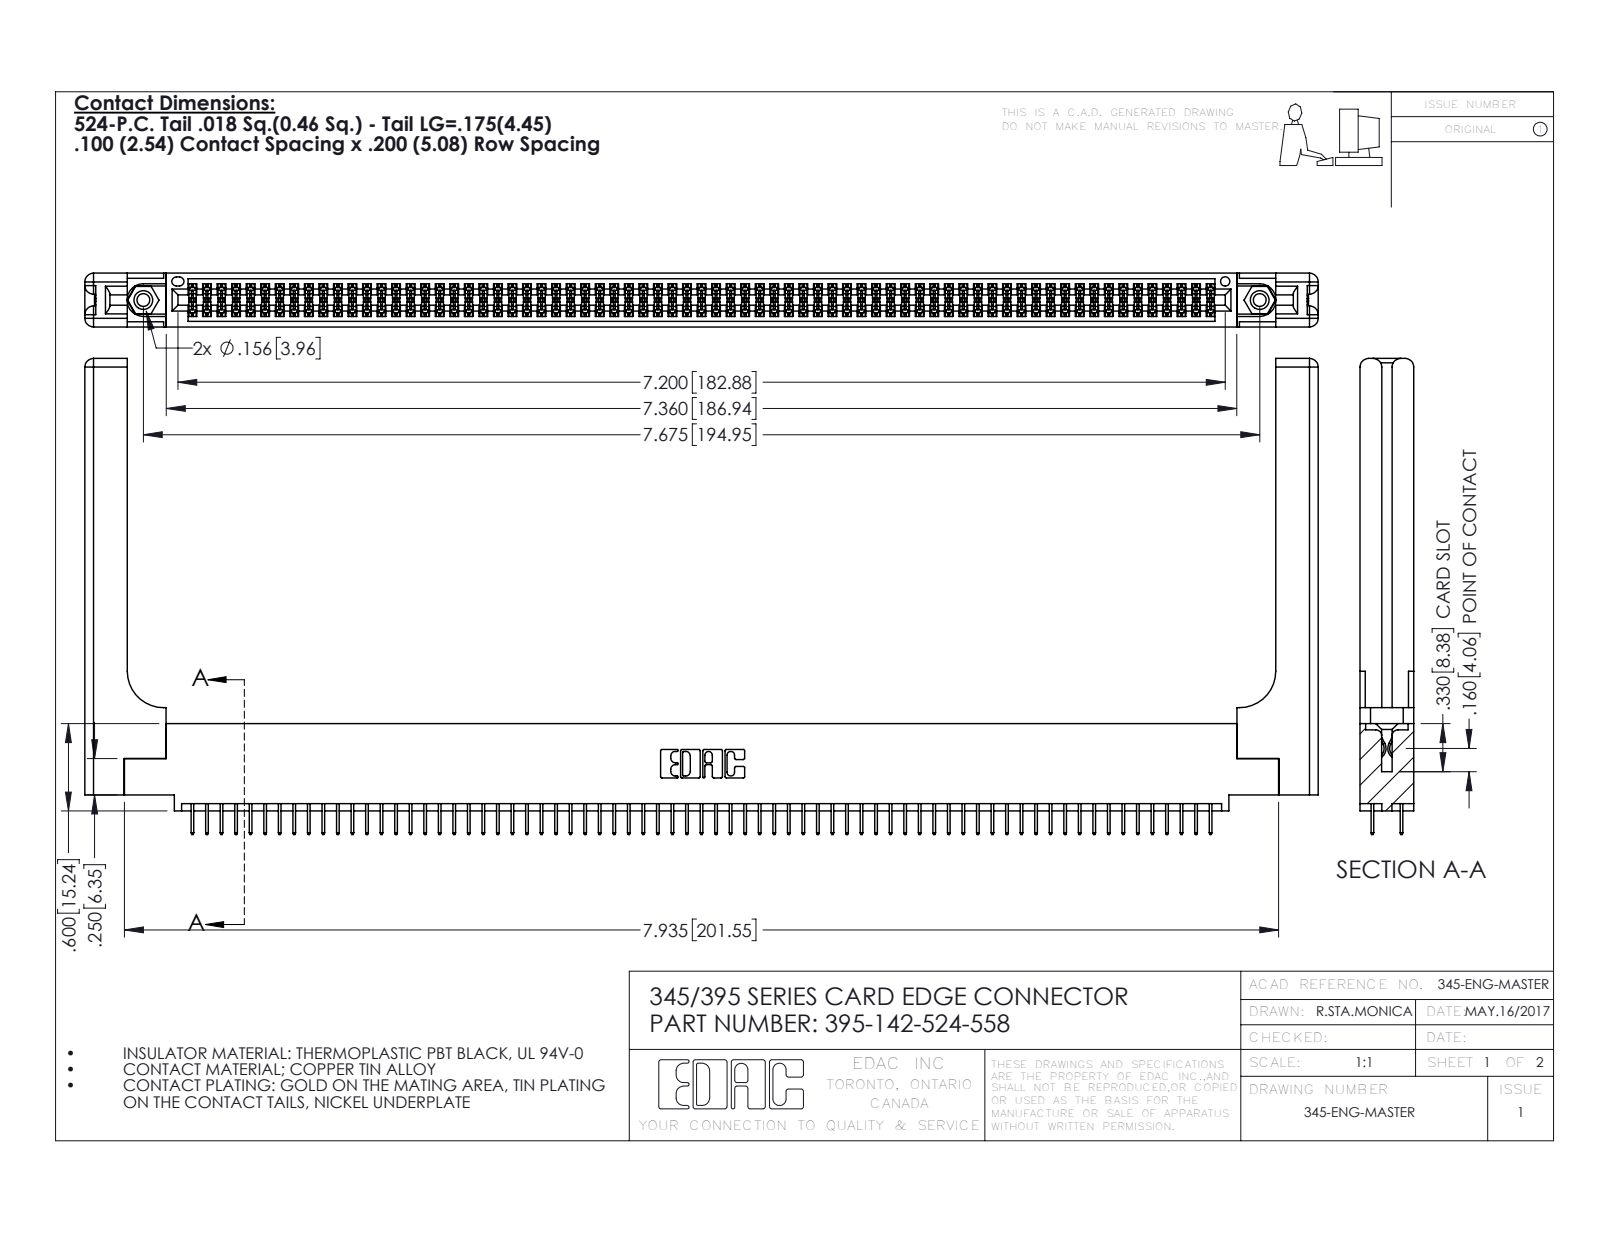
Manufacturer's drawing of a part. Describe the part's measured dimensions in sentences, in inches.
The part is named "345-220-058_345-220-058; 345-292-001_345-293-124; 345 Part_0.110 Offset - 0.156 Dia-TH; 345-250-001_345-250-001-102 (+1 more)". Its 3-D file was written by "SolidWorks 2016 (CONFIG_CONTROL_DESIGN)". It is 147 solids with 8054 faces: 5770 planar, 2224 cylindrical and 60 other. Overall it measures 8.479 by 3.272 by 0.37 inches. Its volume is 1.793 cubic inches and its surface area 55.87 square inches. Round holes: 2 of diameter 0.089, 2 of diameter 0.125, 2 of diameter 0.156, 1 of diameter 0.064. Round bosses or shafts: 2 of diameter 0.155. Partial cylindrical surfaces (rounded edges, fillets, slot ends): 213 of radius 0.006, 22 of radius 0.01, 16 of radius 0.06, 6 of radius 0.007, 6 of radius 0.031, 3 of radius 0.026, 2 of radius 0.014, 2 of radius 0.019. The main face-to-face distances are 0.072, 0.298, 0.37, 0.2, 0.098, 0.272, 0.025, 0.225, 0.072, 0.148. The hole center spacings are 0.27, 7.439, 7.675.
